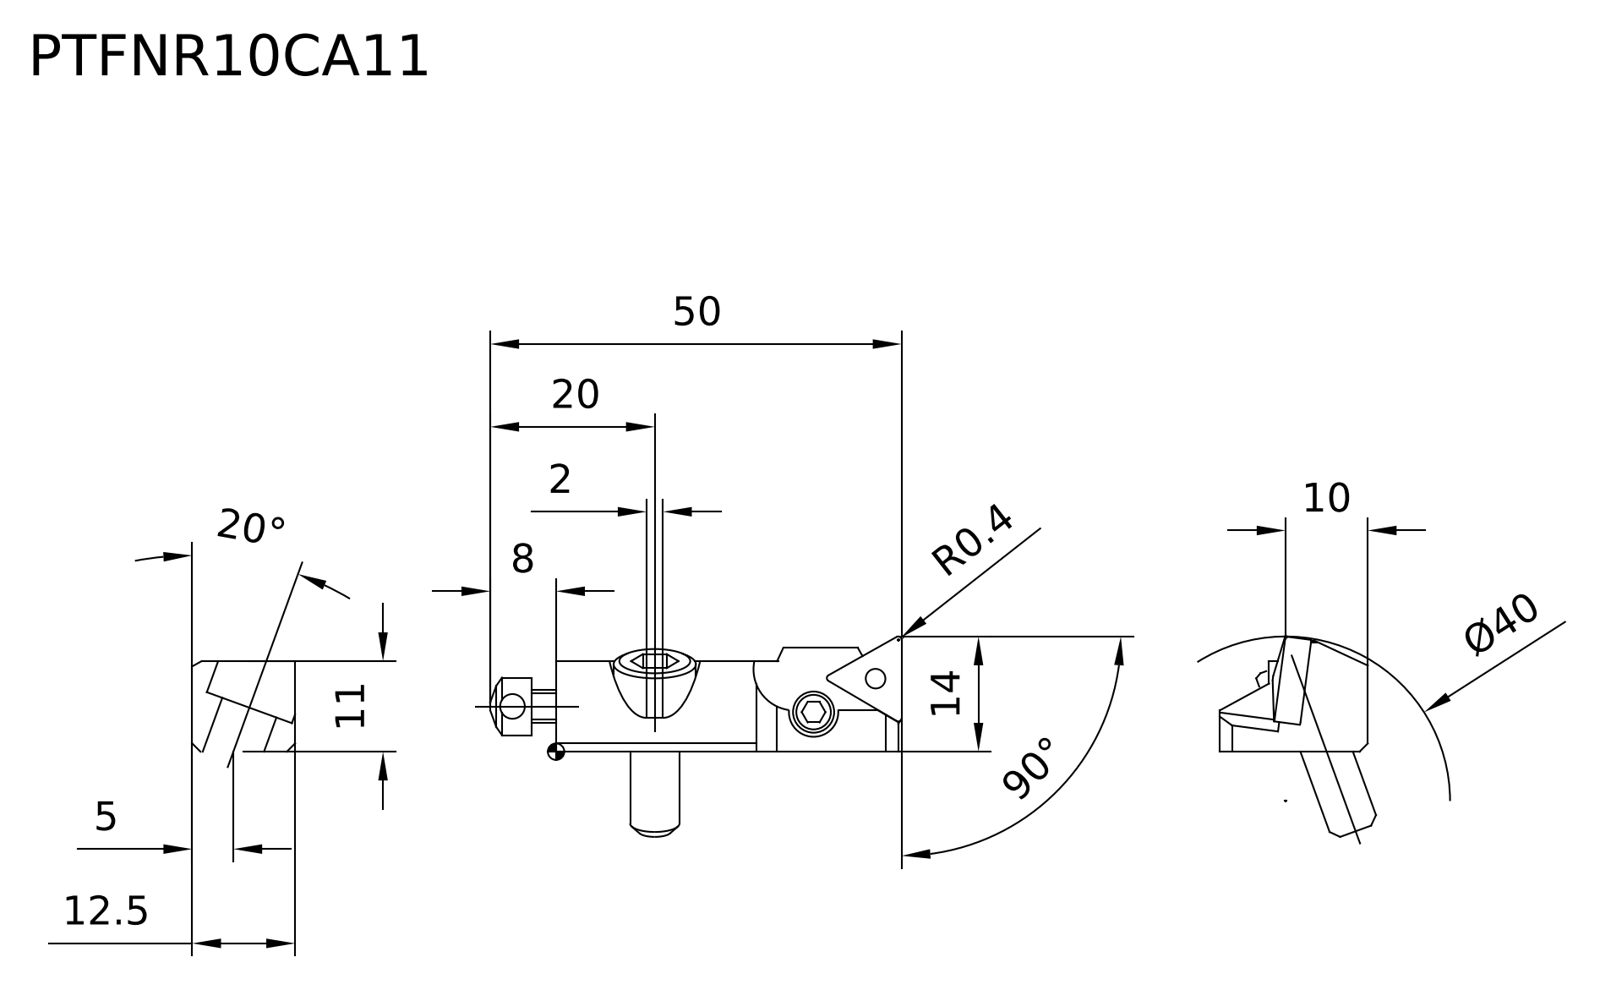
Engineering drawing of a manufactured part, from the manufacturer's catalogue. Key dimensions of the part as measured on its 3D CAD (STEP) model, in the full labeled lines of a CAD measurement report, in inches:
Part name (STEP PRODUCT): PTFNR10CA11_ASM
STEP written by: SIEMENS PLM Software NX 10.0 (AUTOMOTIVE_DESIGN)
Units: inches
Bodies: 7 solids, 220 faces (110 planar, 68 cylindrical, 42 other)
Overall size (bounding box): 1.953 × 0.939 × 0.748
Volume: 0.352 in³ · Surface area: 6.849 in²
Round holes (diameter × count): ⌀0.071 ×2, ⌀0.165 ×2, ⌀0.081 ×1, ⌀0.13 ×1
Round bosses / shafts (diameter × count): ⌀0.197 ×2, ⌀0.394 ×1, ⌀0.276 ×1, ⌀0.236 ×1, ⌀0.157 ×1, ⌀0.118 ×1, ⌀0.083 ×1, ⌀0.067 ×1
Partial cylindrical surfaces — rounded edges, fillets, slot ends (radius × count): R0.008 ×12, R0.079 ×5, R0.02 ×4, R0.138 ×2, R0.217 ×2, R0.059 ×1, R0.067 ×1, R0.069 ×1
Main face-to-face distances: 0.433, 0.486, 1.638, 0.118, 0.709, 0.222, 0.057, 0.49, 0.236, 0.134
Hole centre spacings: 1.72
